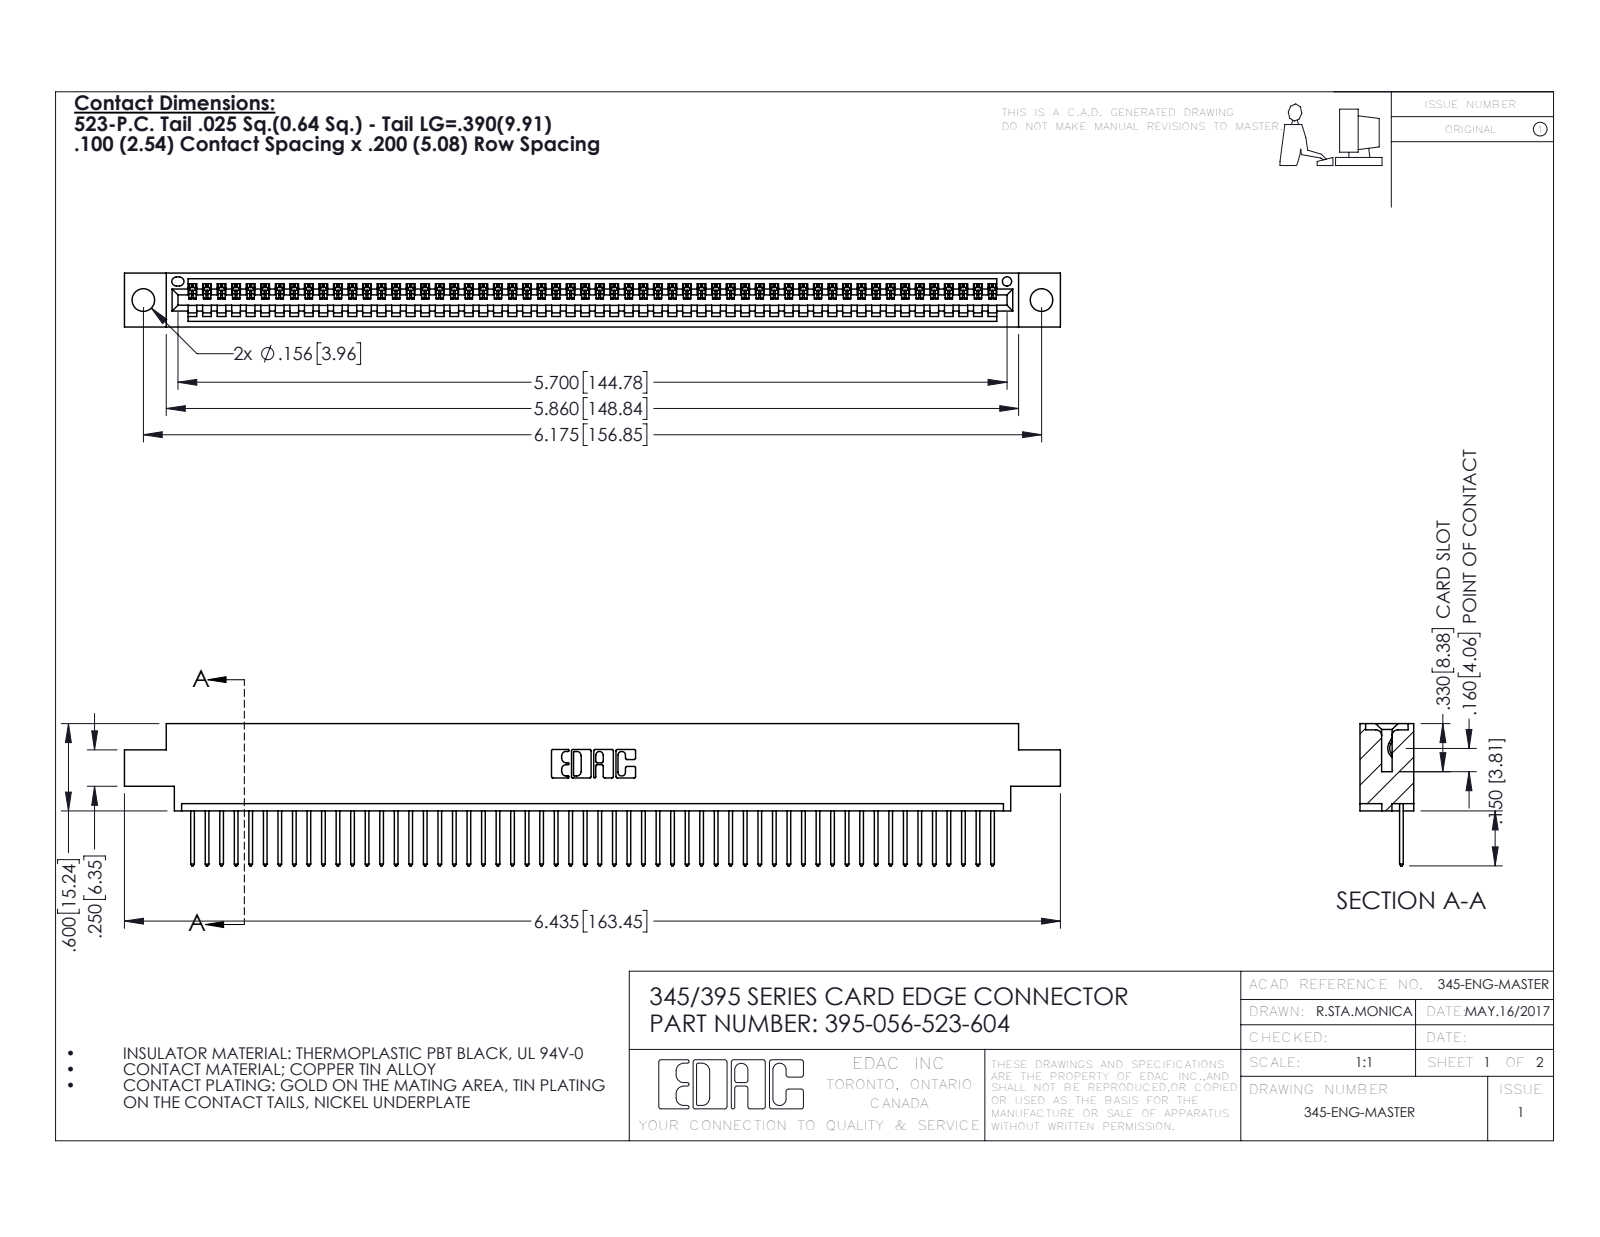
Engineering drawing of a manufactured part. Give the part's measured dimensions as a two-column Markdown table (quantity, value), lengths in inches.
| quantity | value |
| --- | --- |
| part name | 345 Part_0.170 Offset - 0.156 Dia-TH; 395-056-523-604; 345-292-001_345-293-123 |
| STEP written by | SolidWorks 2016 (CONFIG_CONTROL_DESIGN) |
| units | inches |
| bodies | 57 solids, 3378 faces (2324 planar, 1054 cylindrical, 0 other) |
| overall size | 6.435 × 0.977 × 0.37 |
| volume | 0.941 in³ |
| surface area | 32.04 in² |
| round holes (diameter × count) | 0.156 × 2, 0.064 × 1 |
| partial cylindrical surfaces (radius × count) | 0.006 × 112, 0.01 × 112, 0.01 × 22, 0.007 × 6, 0.031 × 6, 0.026 × 3, 0.031 × 2, 0.04 × 2 |
| main face-to-face distances | 0.298, 0.072, 0.37, 0.098, 0.272, 0.025, 0.2, 0.225, 0.175, 0.149 |
| hole center spacings | 0.27, 5.939, 6.175 |
